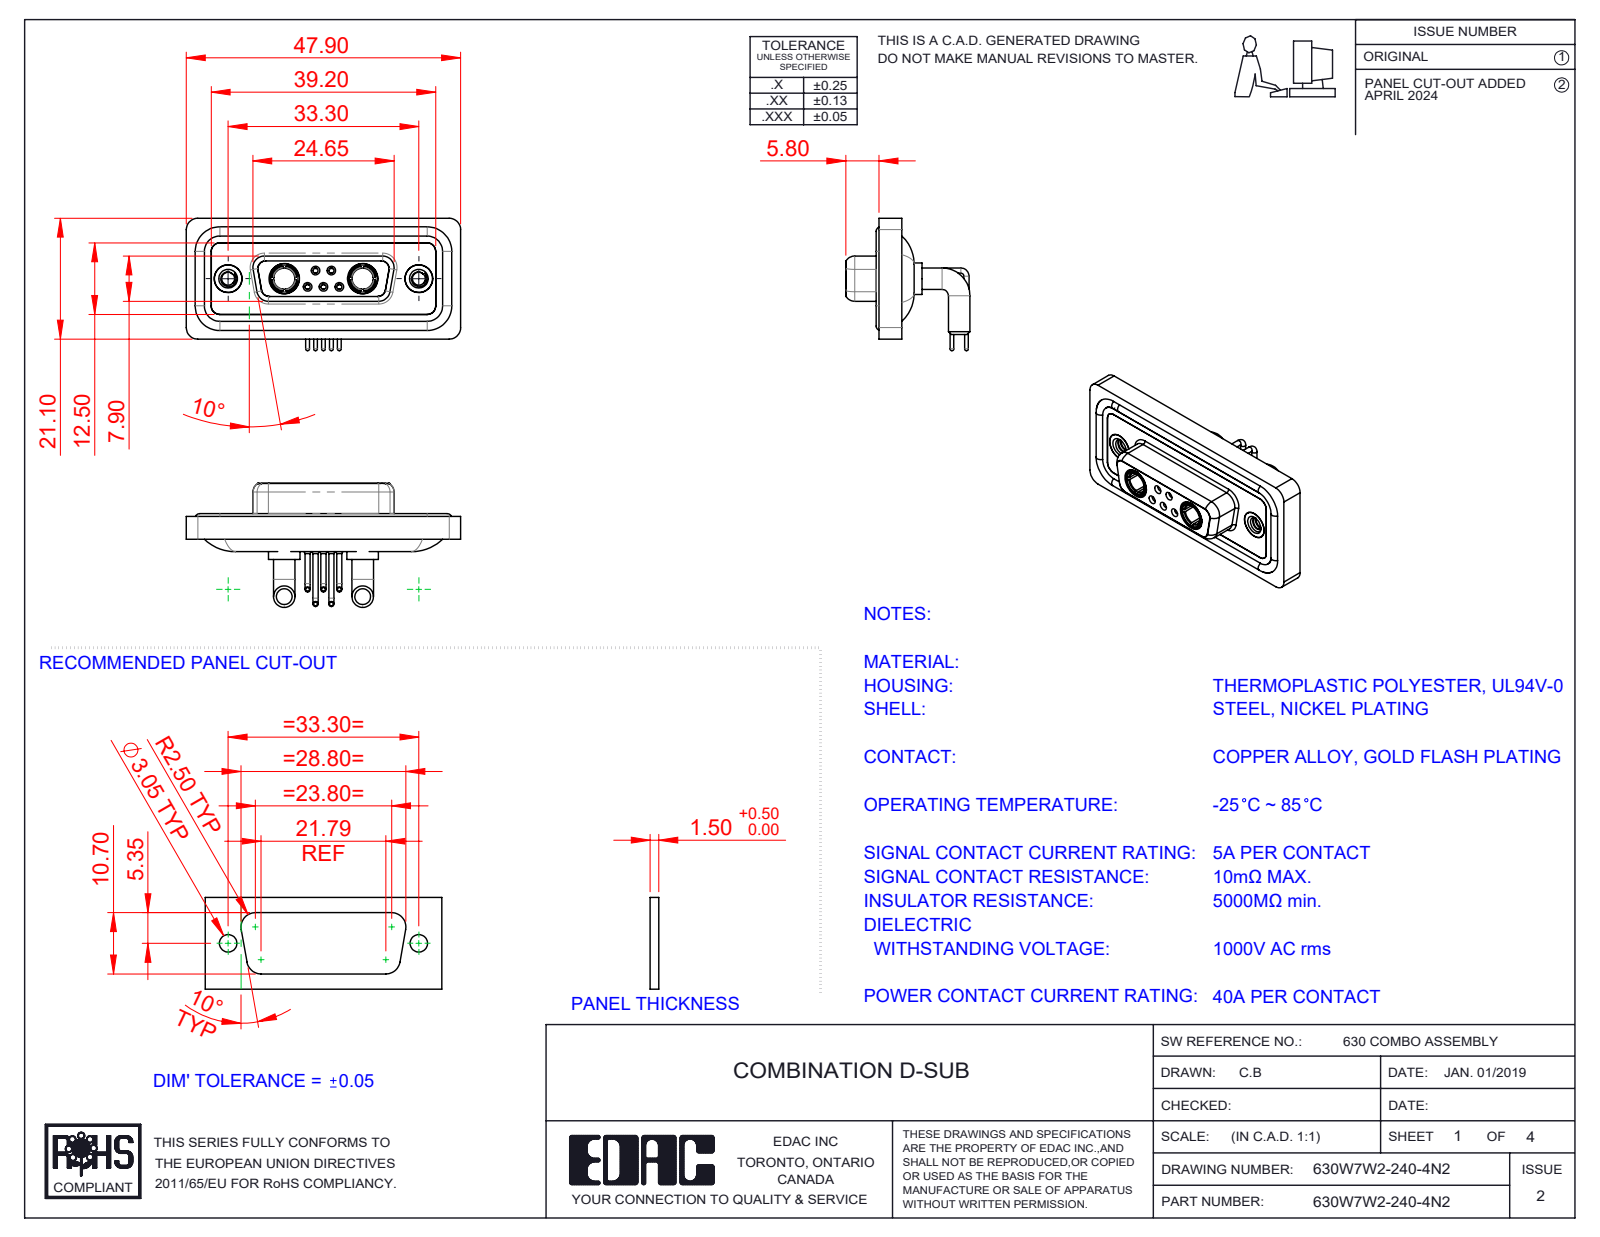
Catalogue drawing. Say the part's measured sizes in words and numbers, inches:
The part is named "630Combo Shell Rear_15 Contacts; 630Combo Waterproof Housing_15 Contacts; 630W7W2-240-4N2; 630Combo Contact Row 1_50 Contacts (+5 more)". Its 3-D file was written by "SolidWorks 2023 (CONFIG_CONTROL_DESIGN)". It is 16 solids with 807 faces: 238 planar, 353 cylindrical and 216 other. Overall it measures 1.886 by 0.91 by 0.854 inches. Its volume is 0.387 cubic inches and its surface area 15.95 square inches. Round holes: 5 of diameter 0.035, 5 of diameter 0.043, 5 of diameter 0.059, 5 of diameter 0.079, 4 of diameter 0.191, 3 of diameter 0.063, 2 of diameter 0.067, 2 of diameter 0.089, 2 of diameter 0.146, 2 of diameter 0.157, 2 of diameter 0.159, 2 of diameter 0.197. Round bosses or shafts: 6 of diameter 0.063, 5 of diameter 0.035, 5 of diameter 0.026, 4 of diameter 0.148, 2 of diameter 0.217, 2 of diameter 0.205, 2 of diameter 0.195, 2 of diameter 0.195. Partial cylindrical surfaces (rounded edges, fillets, slot ends): 20 of radius 0.079, 18 of radius 0.059, 12 of radius 0.053, 8 of radius 0.063, 4 of radius 0.01, 4 of radius 0.02, 4 of radius 0.024, 4 of radius 0.026. The main face-to-face distances are 0.016, 0.071, 0.043, 0.063, 0.098, 0.114, 0.122, 0.146, 0.161, 0.059. The hole center spacings are 0.124, 0.109, 0.386, 0.925, 0.17, 0.17, 0.198, 0.198.
